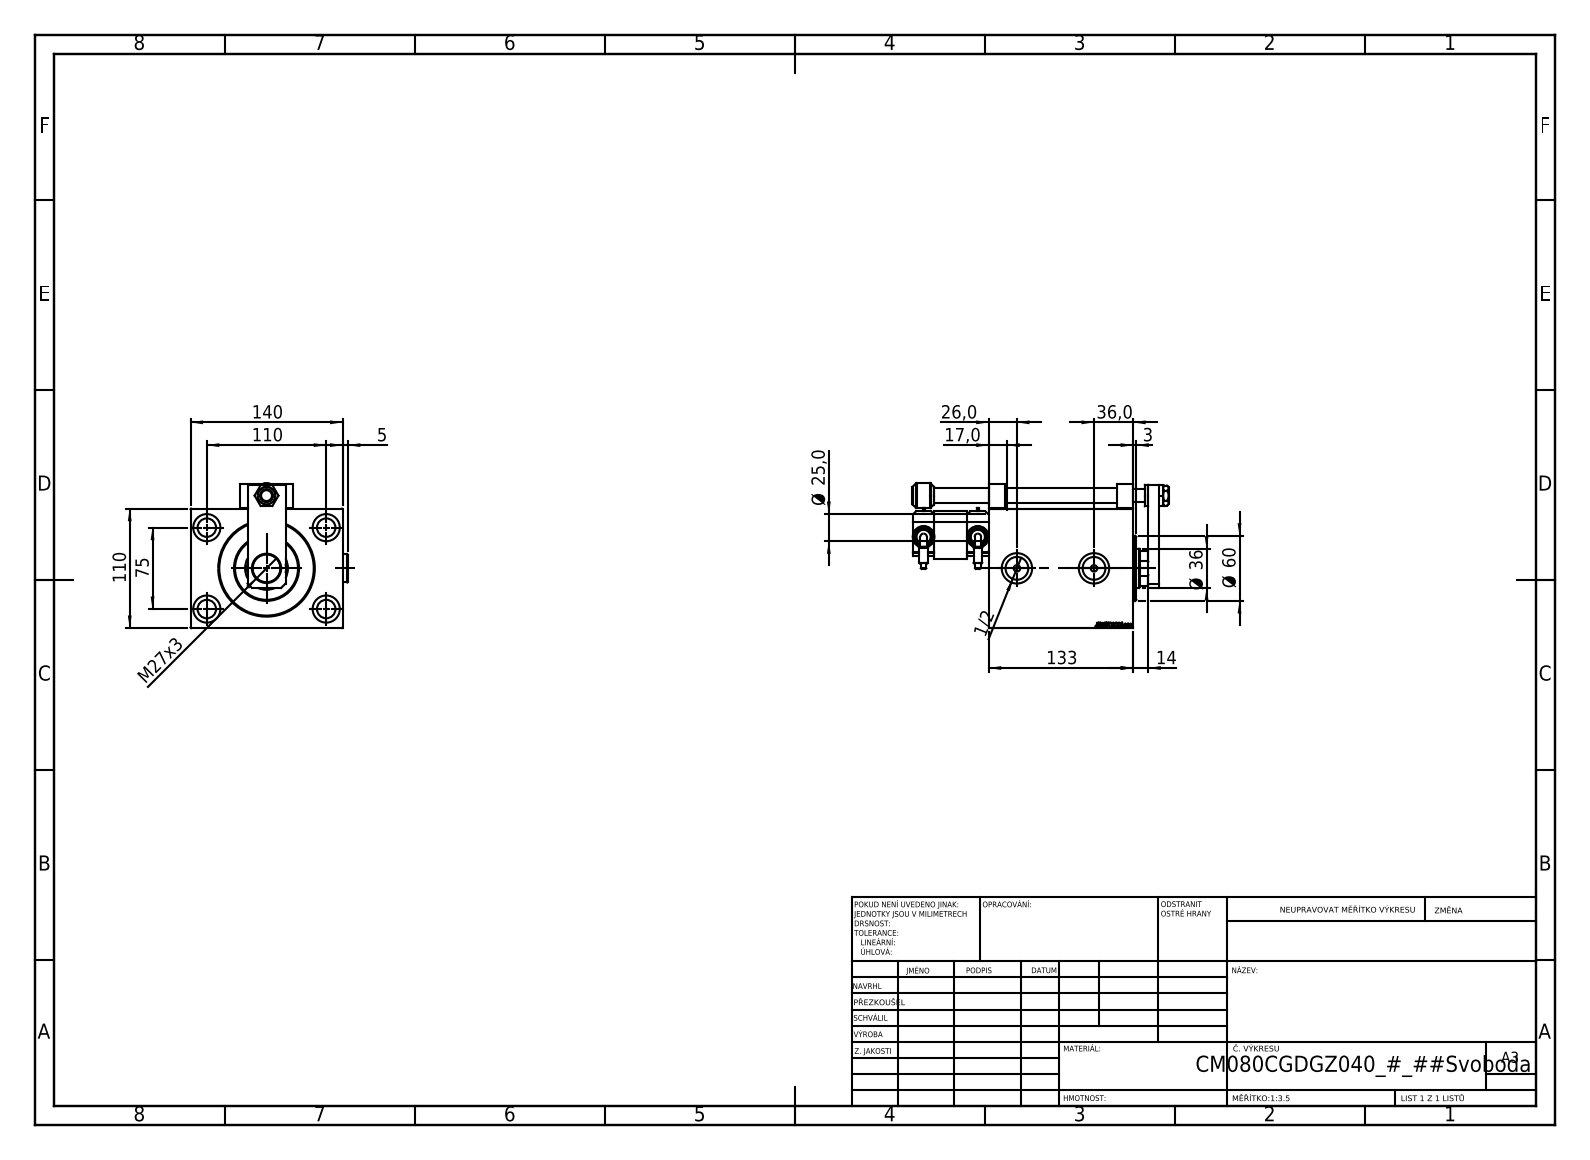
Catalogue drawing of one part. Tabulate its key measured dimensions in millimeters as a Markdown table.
| quantity | value |
| --- | --- |
| part name | ZARAZKA_P; V450CM_VC_B; SWITCH P; NUT_D16 (+7 more) |
| STEP written by | SolidWorks 2019 (CONFIG_CONTROL_DESIGN) |
| units | millimeters |
| bodies | 16 solids, 1172 faces (559 planar, 144 cylindrical, 469 other) |
| overall size | 236 × 144.9 × 133.5 |
| volume | 1 925 000 mm³ |
| surface area | 270 810 mm² |
| round holes (diameter × count) | 4 × 4, 8 × 4, 17 × 4, 25 × 4, 6 × 2, 20.96 × 2, 28 × 2, 12 × 1, 13 × 1, 14 × 1, 25.5 × 1, 27 × 1 |
| round bosses / shafts (diameter × count) | 20 × 3, 26 × 2, 16 × 2, 14 × 2, 8 × 2, 6 × 2, 5.04 × 2, 60 × 1 |
| partial cylindrical surfaces (radius × count) | 3 × 1, 17.5 × 1 |
| main face-to-face distances | 110, 140, 133, 21, 112, 50, 14, 40, 20, 119 |
| hole center spacings | 66.57, 20, 62.41, 75, 110, 118, 118.09, 119.68 |
